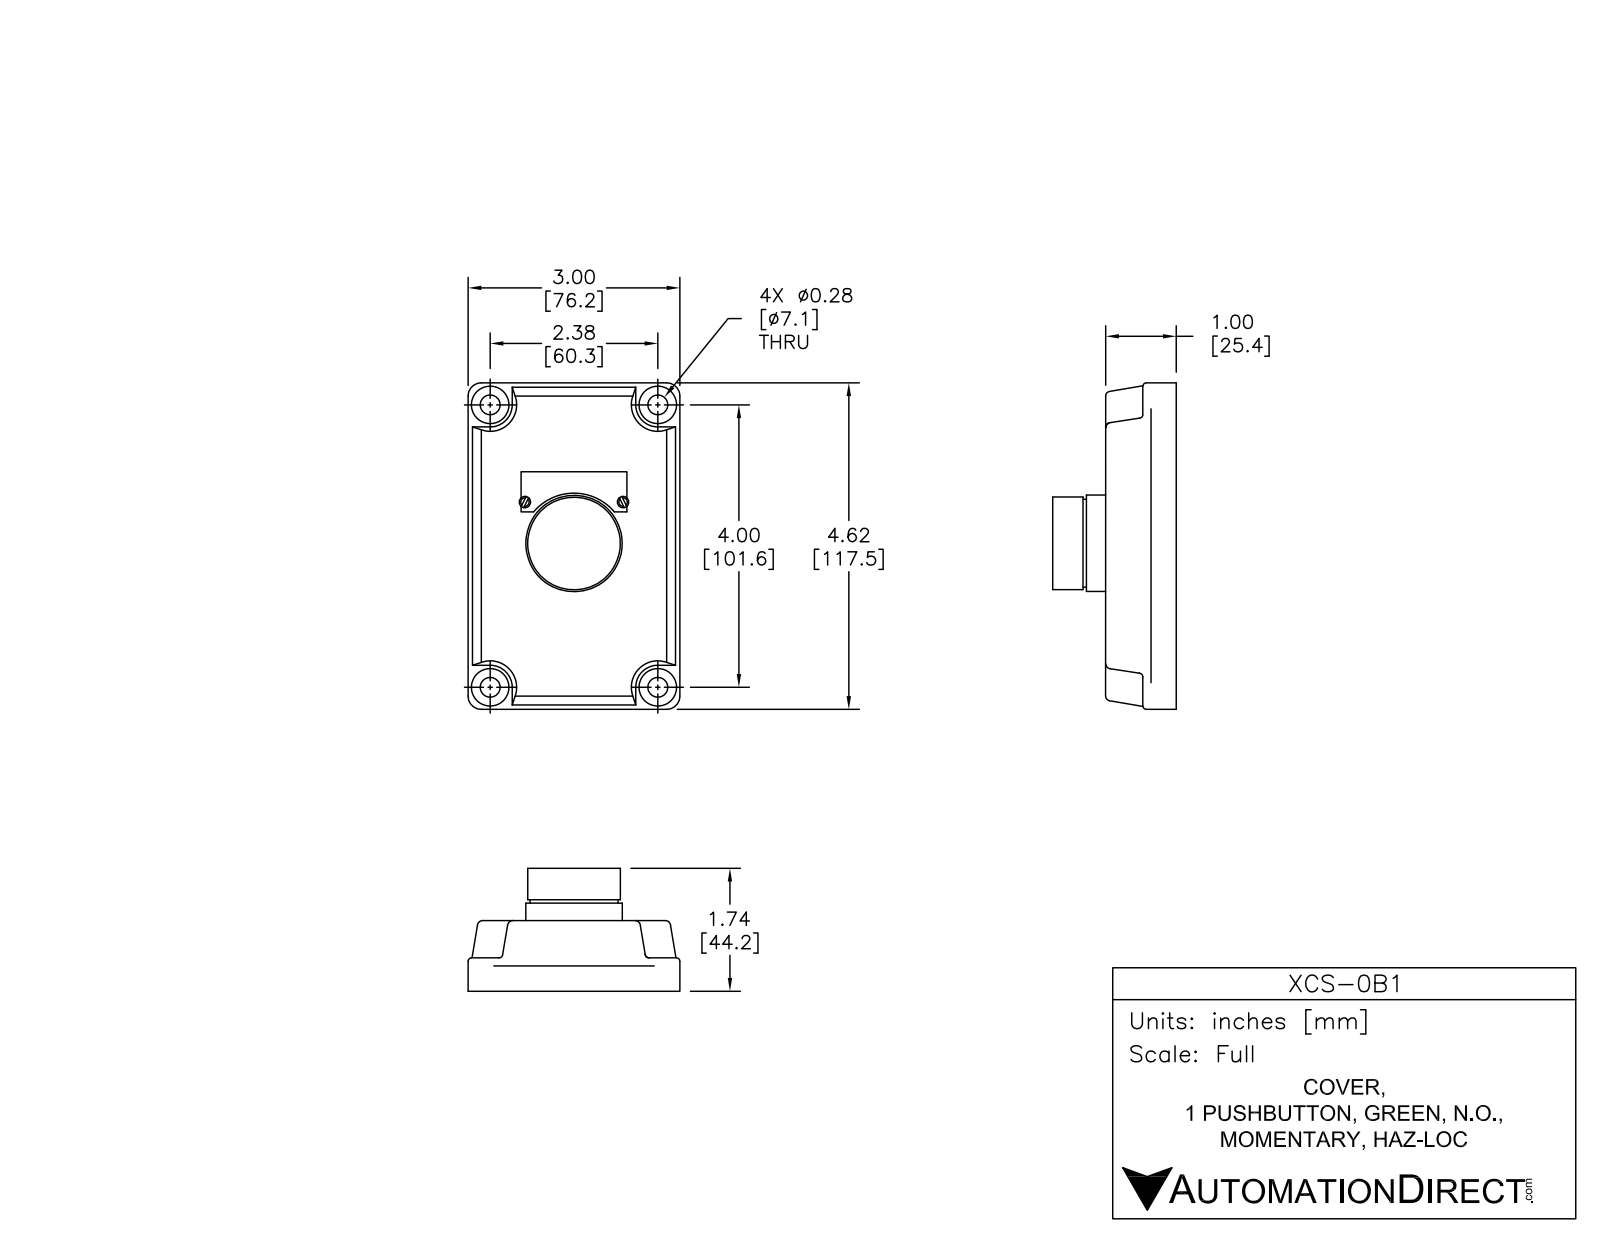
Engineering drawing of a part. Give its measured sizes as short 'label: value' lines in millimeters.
name: XCS-0B1
written by: SolidWorks 2015 (AUTOMOTIVE_DESIGN)
unit: mm
bodies: 10 solids, 470 faces (166 planar, 171 cylindrical, 133 other)
size: 117.6 × 81.1 × 78.74
volume: 207 620 mm³; area: 55 537 mm²
holes: 4× ⌀6.65, 4× ⌀6.86, 1× ⌀28.5
bosses: 6× ⌀3.3, 4× ⌀11.6, 4× ⌀6.35, 1× ⌀35, 1× ⌀32.06, 1× ⌀26.25
rounds: 28× R0.25, 10× R1.27, 8× R0.51, 8× R1.4, 8× R3, 4× R2.38, 4× R2.54, 4× R9.65
face distances: 13.34, 12.7, 26.04, 11.3, 24, 37.34, 17.5, 6.5, 4.8, 30.84
hole spacings: 59.11, 10.2, 20.4, 60.46, 101.6, 118.23, 10.13, 10.18
